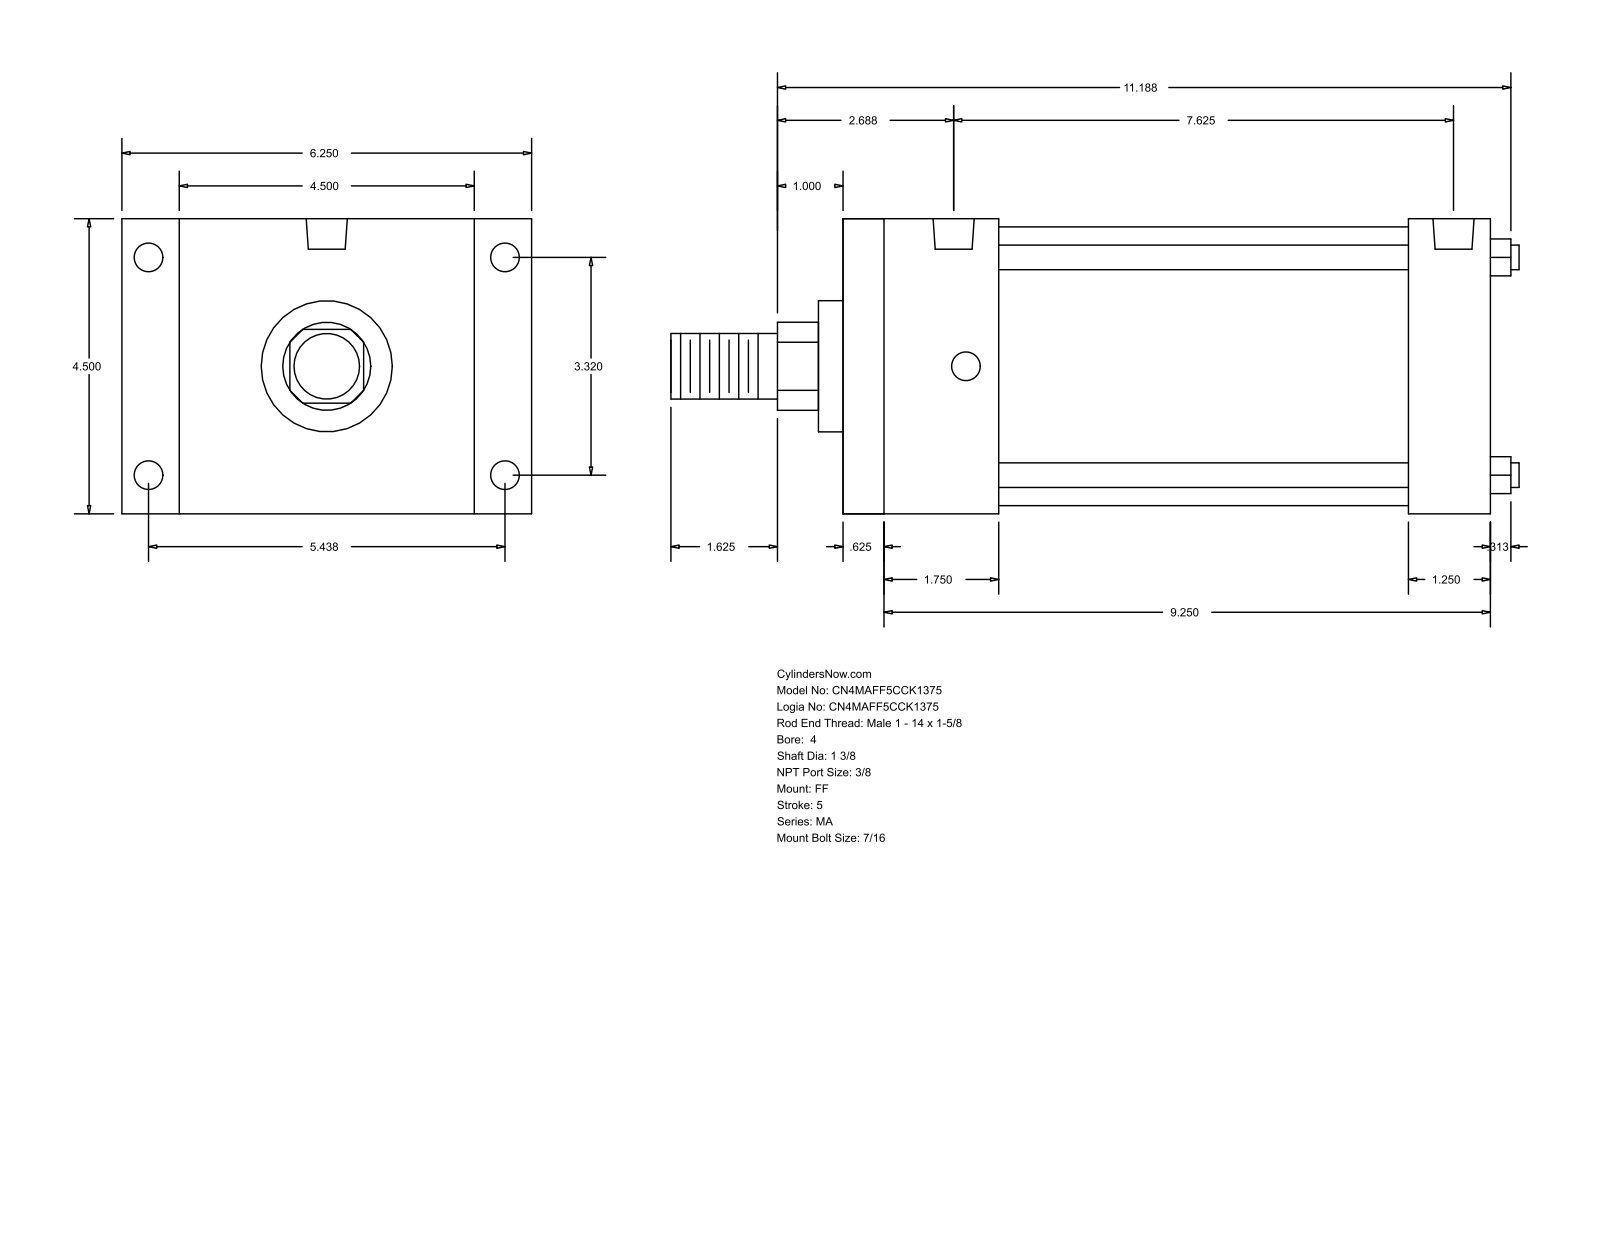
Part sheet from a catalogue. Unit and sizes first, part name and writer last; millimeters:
Units: millimetres
Overall size (bounding box): 328.61 × 158.75 × 114.3
Round holes (diameter × count): ⌀11.11 ×8, ⌀15.93 ×2
Round bosses / shafts (diameter × count): ⌀9.53 ×4, ⌀107.95 ×1, ⌀50.8 ×1, ⌀34.92 ×1, ⌀25.4 ×1
Partial cylindrical surfaces — rounded edges, fillets, slot ends (radius × count): R17.06 ×1
Main face-to-face distances: 114.3, 250.83, 15.87, 234.96, 22.23, 136.53, 219.07, 203.2, 31.76, 60.32
Hole centre spacings: 84.32, 138.12, 161.82, 184.15, 4.76, 4.77, 188.91, 188.92
Bodies: 0 solids, 92 faces (64 planar, 28 cylindrical, 0 other)
Part name (STEP PRODUCT): MA_FF__0400_1.375
STEP written by: GSSL Pune (CONFIG_CONTROL_DESIGN)
